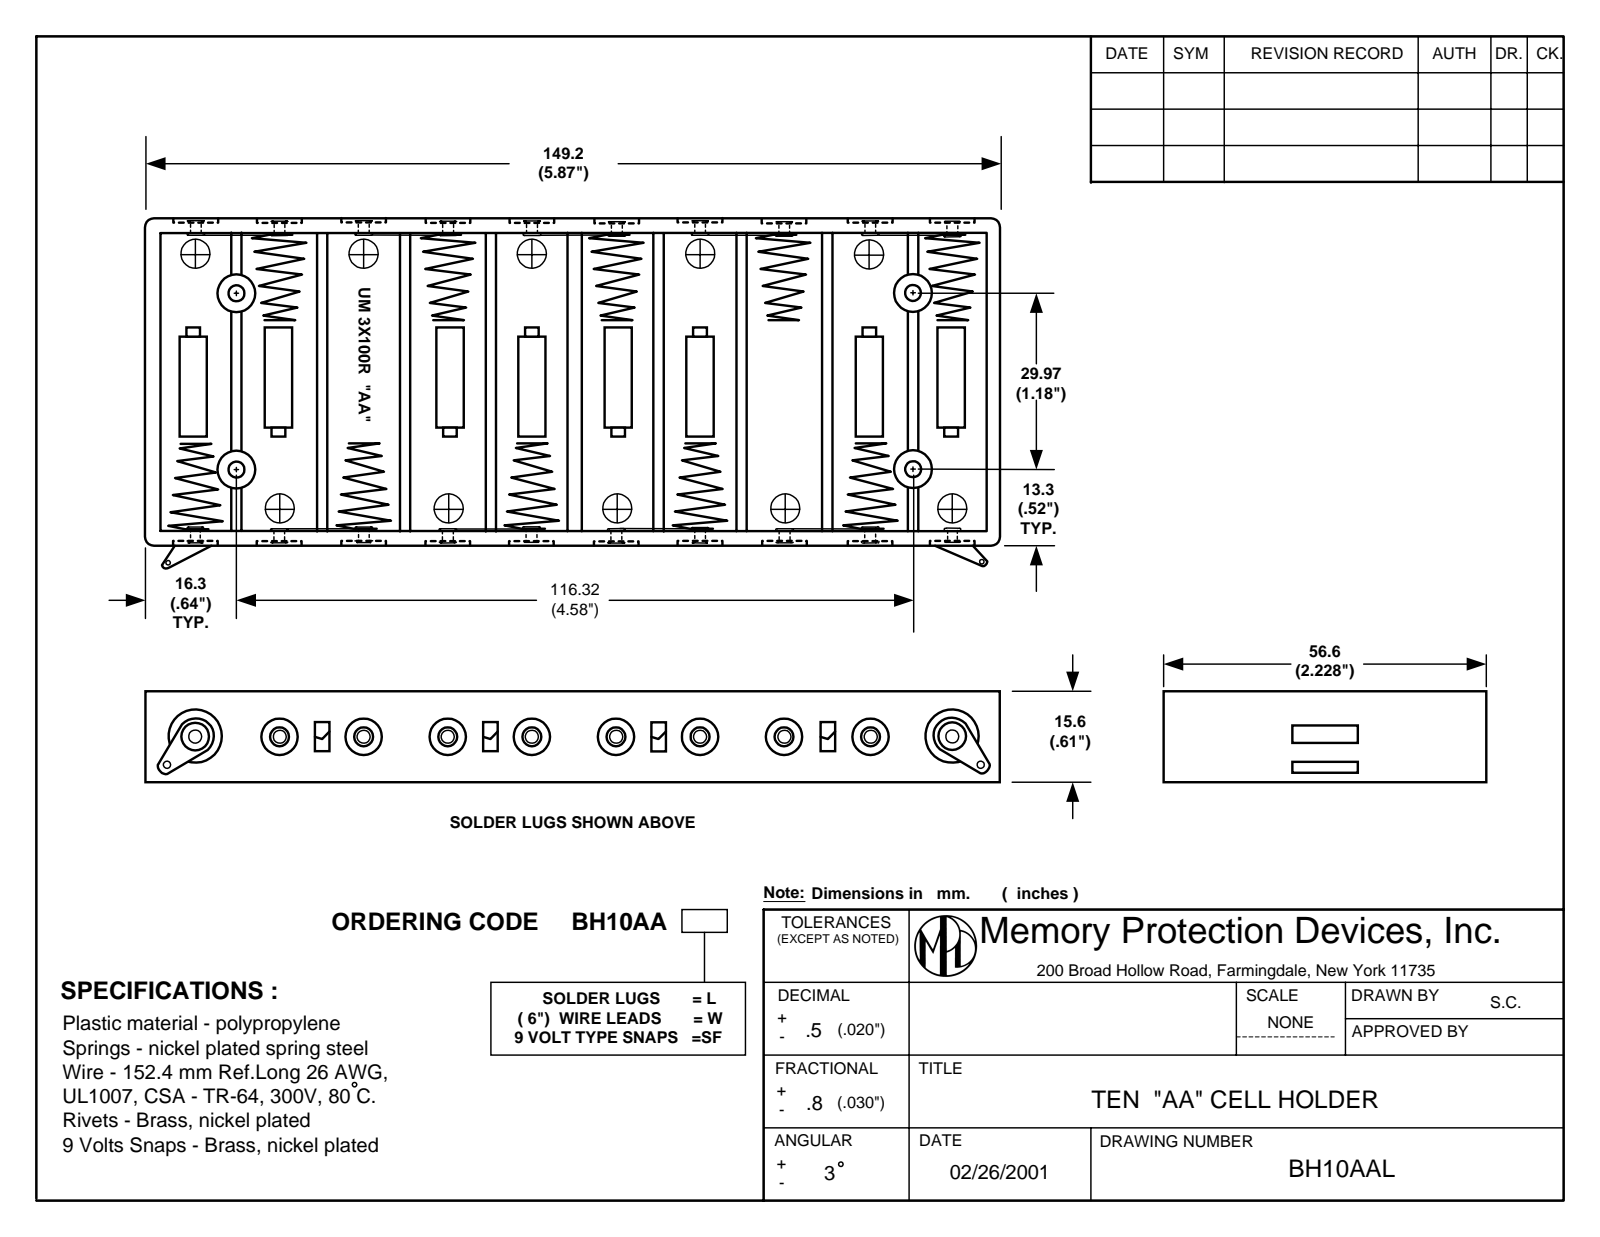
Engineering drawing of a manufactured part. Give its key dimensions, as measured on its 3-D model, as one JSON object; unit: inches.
{"part_name": "BH10AAL", "step_written_by": "SolidWorks 2017 (AUTOMOTIVE_DESIGN)", "units": "inches", "bodies": {"solids": 32, "faces": 1149, "planar": 551, "cylindrical": 347, "other": 251}, "overall_size": [5.961, 2.313, 0.614], "volume_in3": 1.939, "surface_area_in2": 56.41, "round_holes": [[0.157, 16], [0.063, 11], [0.087, 10], [0.25, 10], [0.115, 4], [0.254, 4], [0.035, 2], [0.12, 2], [0.185, 1]], "round_bosses_or_shafts": [[0.197, 16], [0.185, 10], [0.031, 2], [0.087, 1]], "partial_cylinders_radius": [[0.047, 2], [0.094, 2], [0.354, 2], [0.358, 2], [0.093, 1]], "face_to_face_distances": [0.067, 0.079, 2.184, 0.134, 2.263, 2.106, 5.883, 2.951, 3.01, 2.872], "hole_center_spacings": [2.902, 1.741, 1.161, 0.58, 0.643, 1.554, 1.682, 2.334]}
